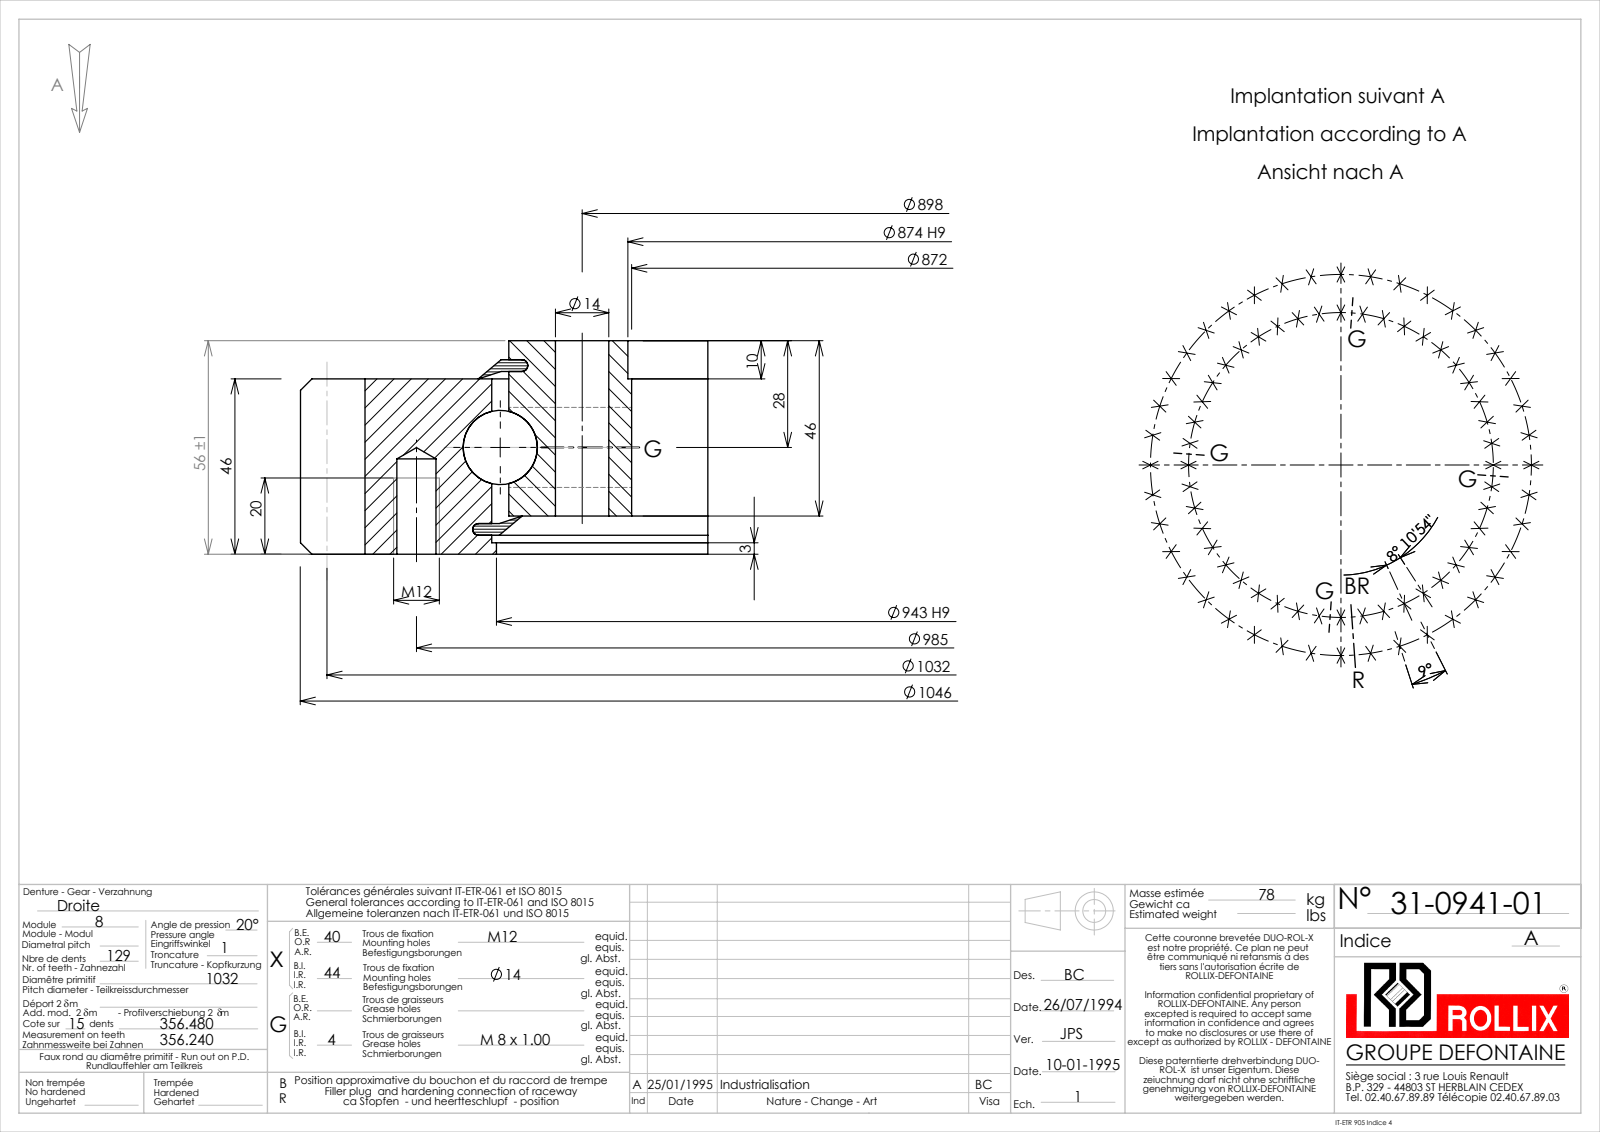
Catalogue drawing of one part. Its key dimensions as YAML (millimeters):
part_name: "31-0941-01"
step_written_by: "SolidWorks 2016 (CONFIG_CONTROL_DESIGN)"
units: millimeters
bodies: {solids: 9, faces: 1180, planar: 312, cylindrical: 461, other: 407}
overall_size: [1045.99, 1045.93, 56]
volume: 9332000
surface_area: 1522000
round_holes:
  - {diameter: 14, count: 44}
  - {diameter: 10.25, count: 40}
  - {diameter: 7, count: 4}
  - {diameter: 872, count: 1}
  - {diameter: 874, count: 1}
  - {diameter: 943, count: 1}
  - {diameter: 945.5, count: 1}
round_bosses_or_shafts:
  - {diameter: 8, count: 4}
  - {diameter: 936.5, count: 1}
partial_cylinders:
  - {radius: 506, count: 1}
  - {radius: 523, count: 1}
face_to_face_distances: [46, 10, 36, 56, 1.95, 5.05, 43, 8.05, 47.95, 37.95]
hole_center_spacings: [77.28, 154.09, 229.95, 936.79, 514.66, 578.97, 639.71, 696.5]
